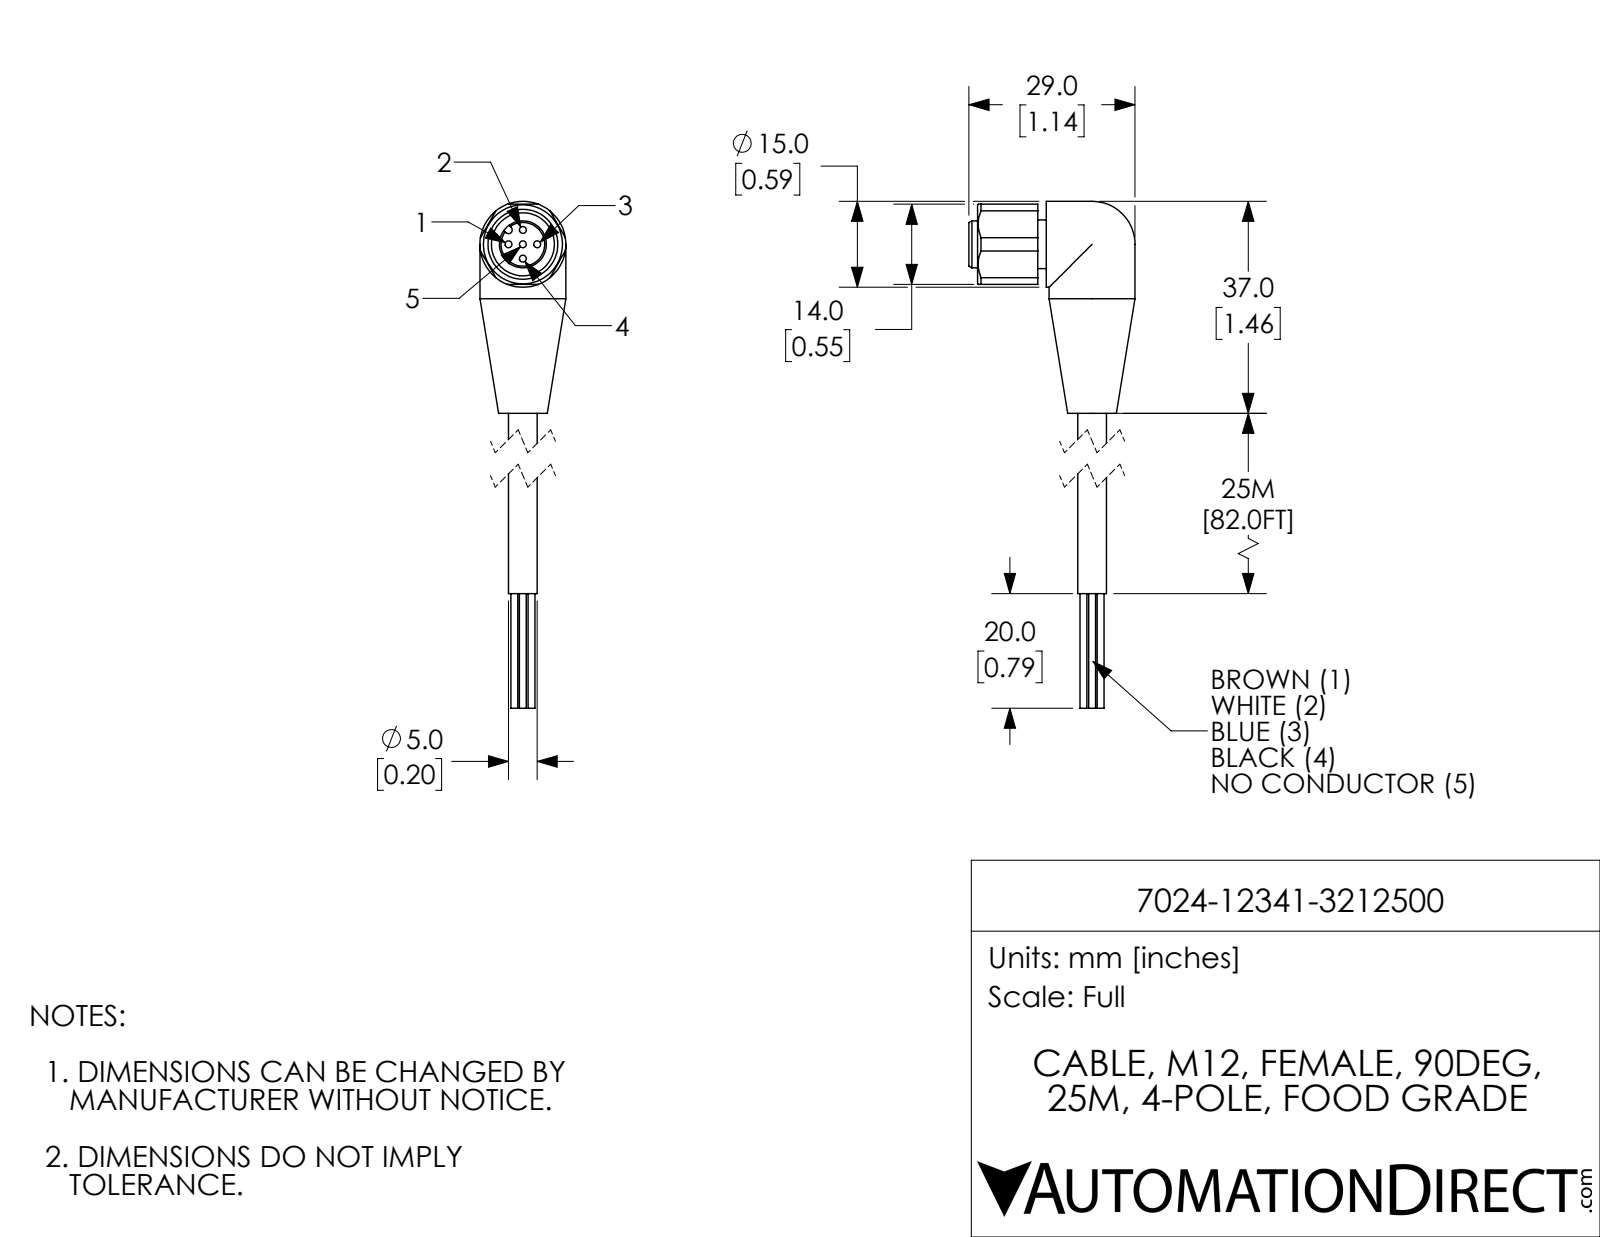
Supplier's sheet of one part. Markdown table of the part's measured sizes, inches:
| quantity | value |
| --- | --- |
| part name | 7024-12341-3212500 |
| STEP written by | SolidWorks 2018 (AUTOMOTIVE_DESIGN) |
| units | inches |
| bodies | 1 solid, 73 faces (25 planar, 38 cylindrical, 10 other) |
| overall size | 3.425 × 1.142 × 0.591 |
| volume | 0.452 in³ |
| surface area | 6.023 in² |
| round holes (diameter × count) | 0.047 × 5, 0.433 × 1 |
| round bosses / shafts (diameter × count) | 0.047 × 4, 0.591 × 2, 0.335 × 1, 0.323 × 1, 0.197 × 1 |
| partial cylindrical surfaces (radius × count) | 0.026 × 1 |
| main face-to-face distances | 0.551, 0.059, 0.472, 0.177, 0.118, 0.531, 0.354, 0.886, 1.437, 0.413 |
| hole center spacings | 0.098, 0.139, 0.197 |
